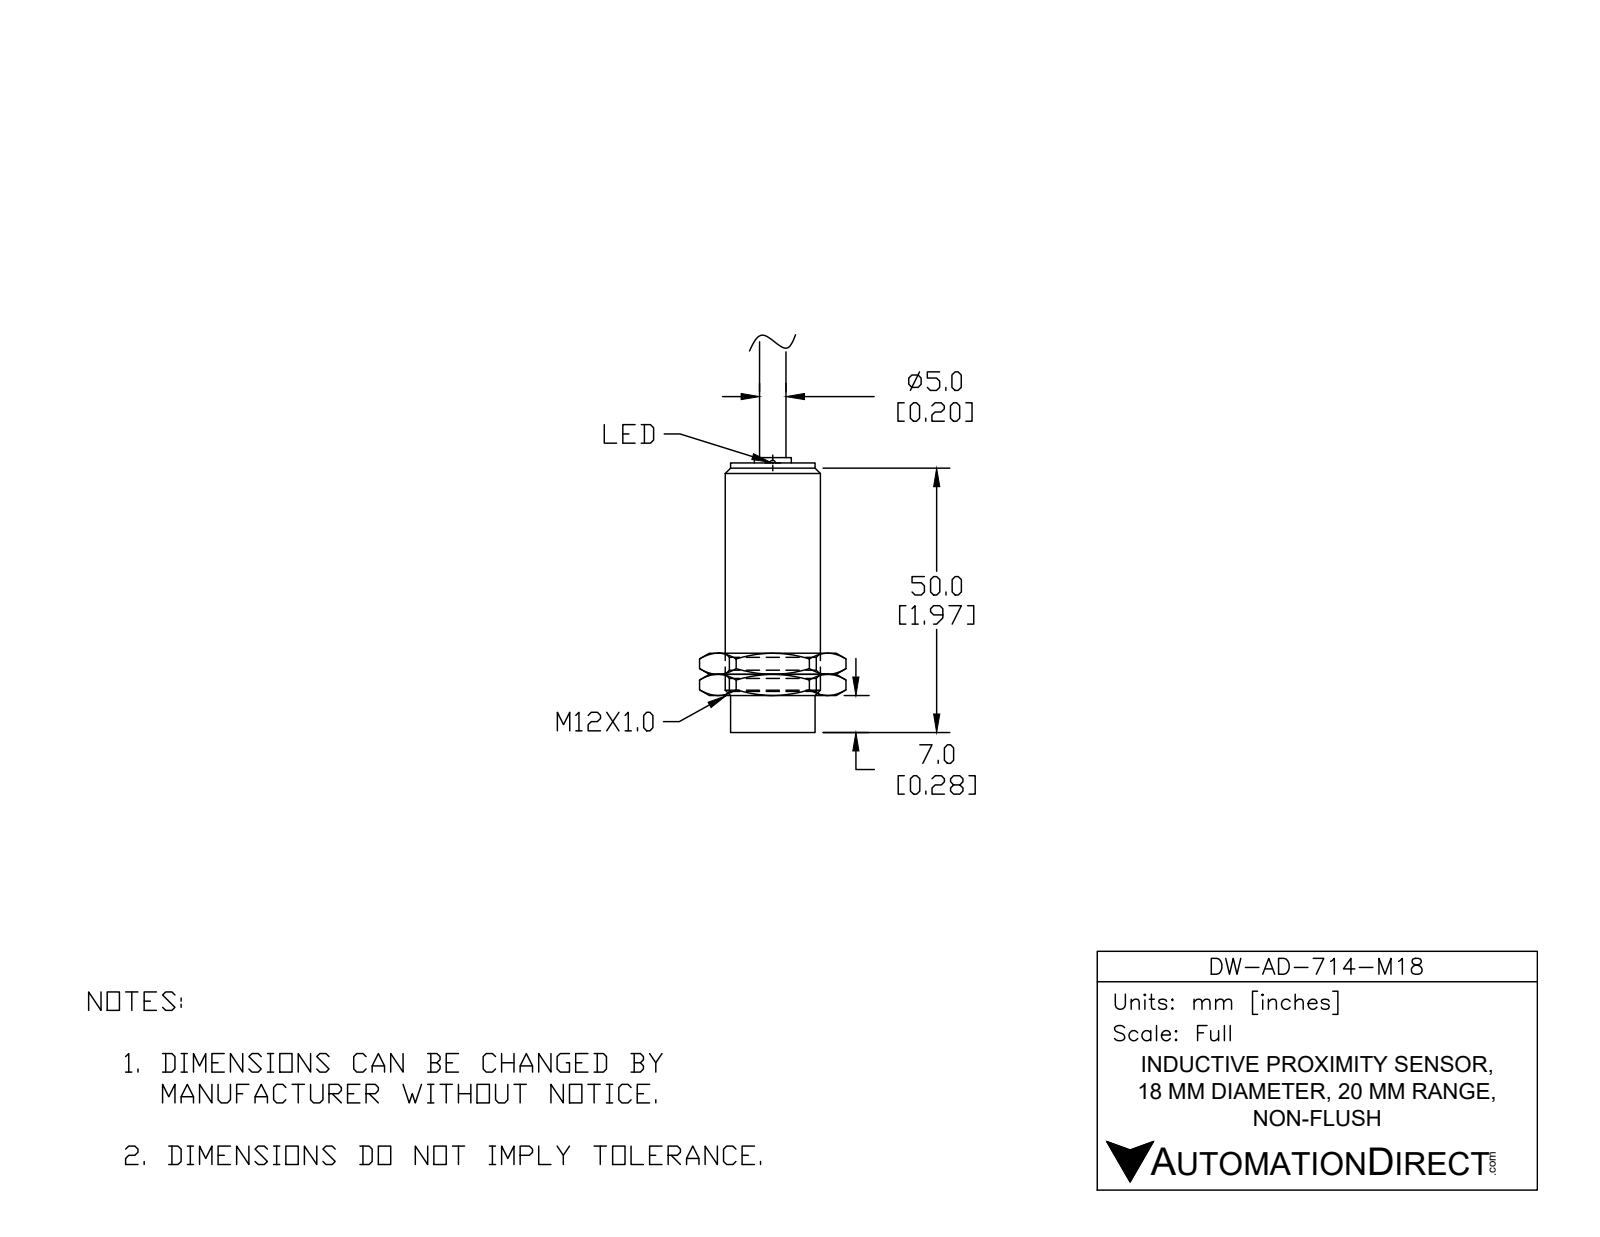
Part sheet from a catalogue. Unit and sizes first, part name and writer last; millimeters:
Units: millimetres
Overall size (bounding box): 76.6 × 18 × 18
Round bosses / shafts (diameter × count): ⌀18 ×1, ⌀16.4 ×1, ⌀10.5 ×1, ⌀6.8 ×1, ⌀5 ×1, ⌀3 ×1
Main face-to-face distances: 51, 0.8, 53, 2, 51.8, 1.2, 48, 3, 3.8, 5
Volume: 13 300 mm³ · Surface area: 3 818 mm²
Bodies: 2 solids, 37 faces (18 planar, 7 cylindrical, 12 other)
Part name (STEP PRODUCT): DW-AD-714-M18
STEP written by: SolidWorks 2017 (AUTOMOTIVE_DESIGN)
